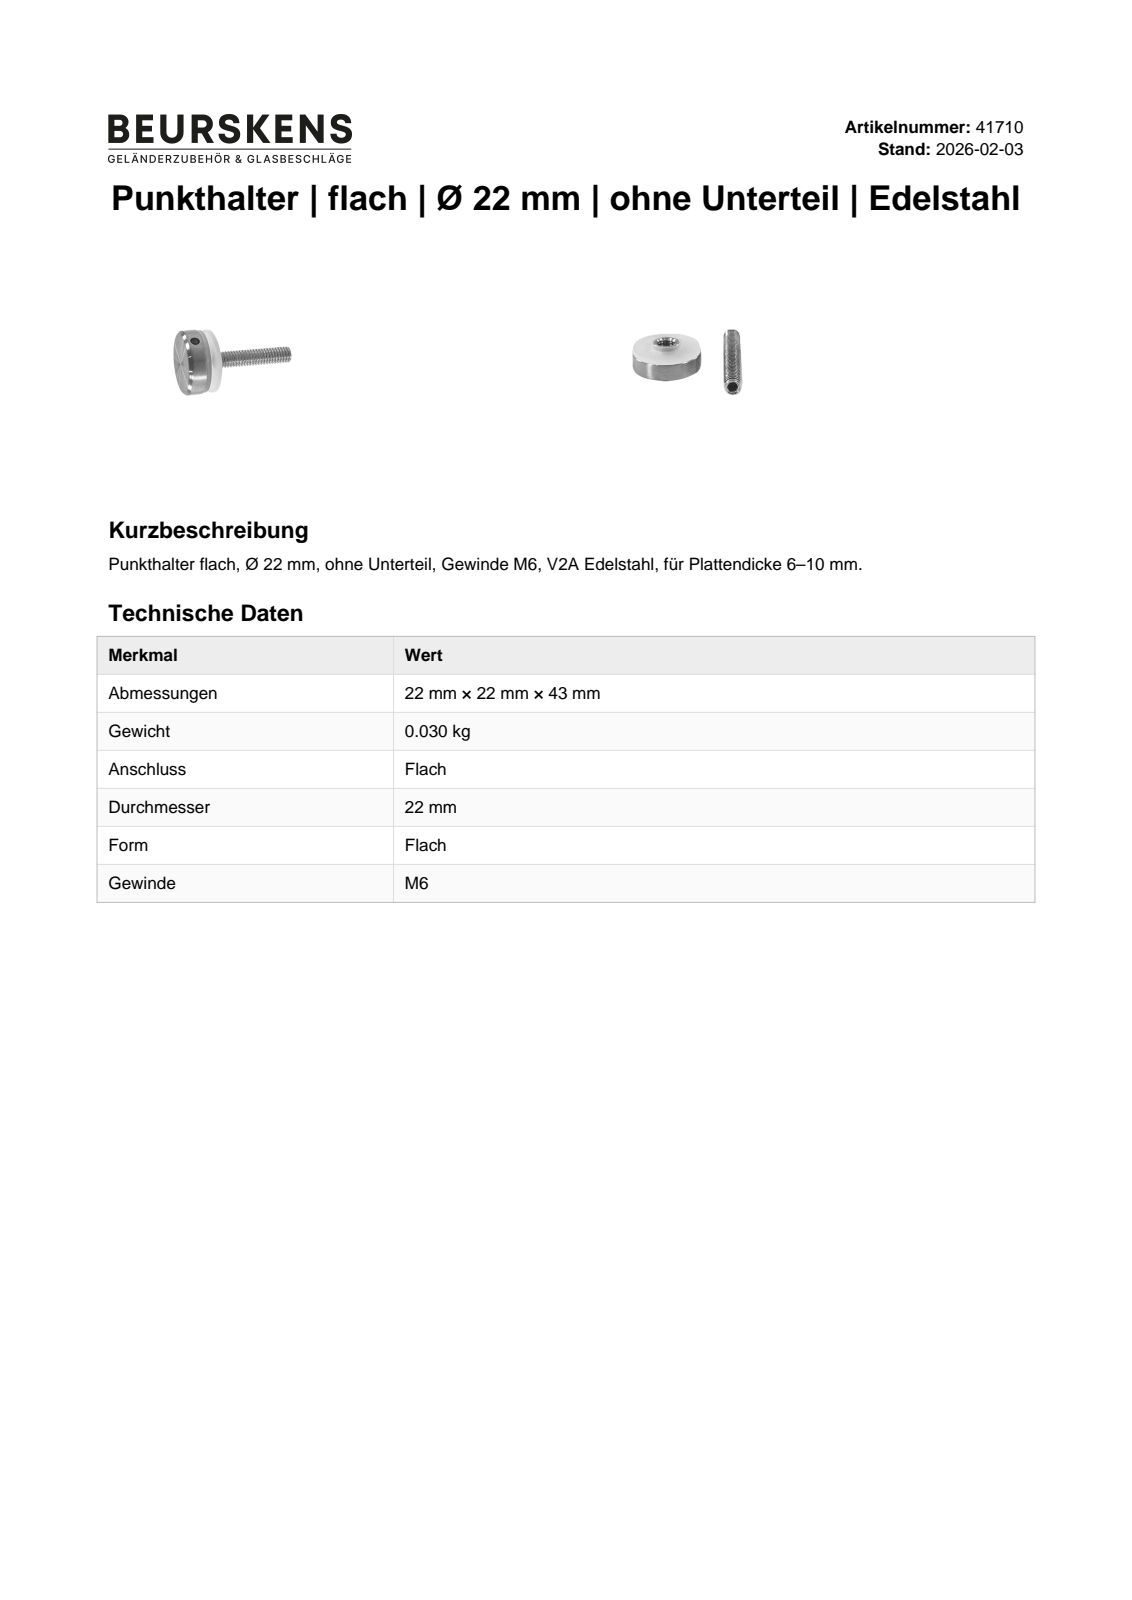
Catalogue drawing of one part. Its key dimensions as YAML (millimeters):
part_name: "41710; 40923; 40913; Gewindestift M6x40mm (+1 more)"
step_written_by: "Autodesk Inventor 2023 (AUTOMOTIVE_DESIGN)"
units: millimeters
bodies: {solids: 4, faces: 33, planar: 19, cylindrical: 10, other: 4}
overall_size: [42.5, 22, 22]
volume: 4209
surface_area: 3753
round_holes:
  - {diameter: 3, count: 1}
  - {diameter: 6, count: 1}
  - {diameter: 8.5, count: 1}
round_bosses_or_shafts:
  - {diameter: 22, count: 1}
  - {diameter: 21, count: 1}
  - {diameter: 9.5, count: 1}
face_to_face_distances: [1.5, 3, 6, 9, 10.5, 4.5, 7.5, 5, 2.5, 3.5]
